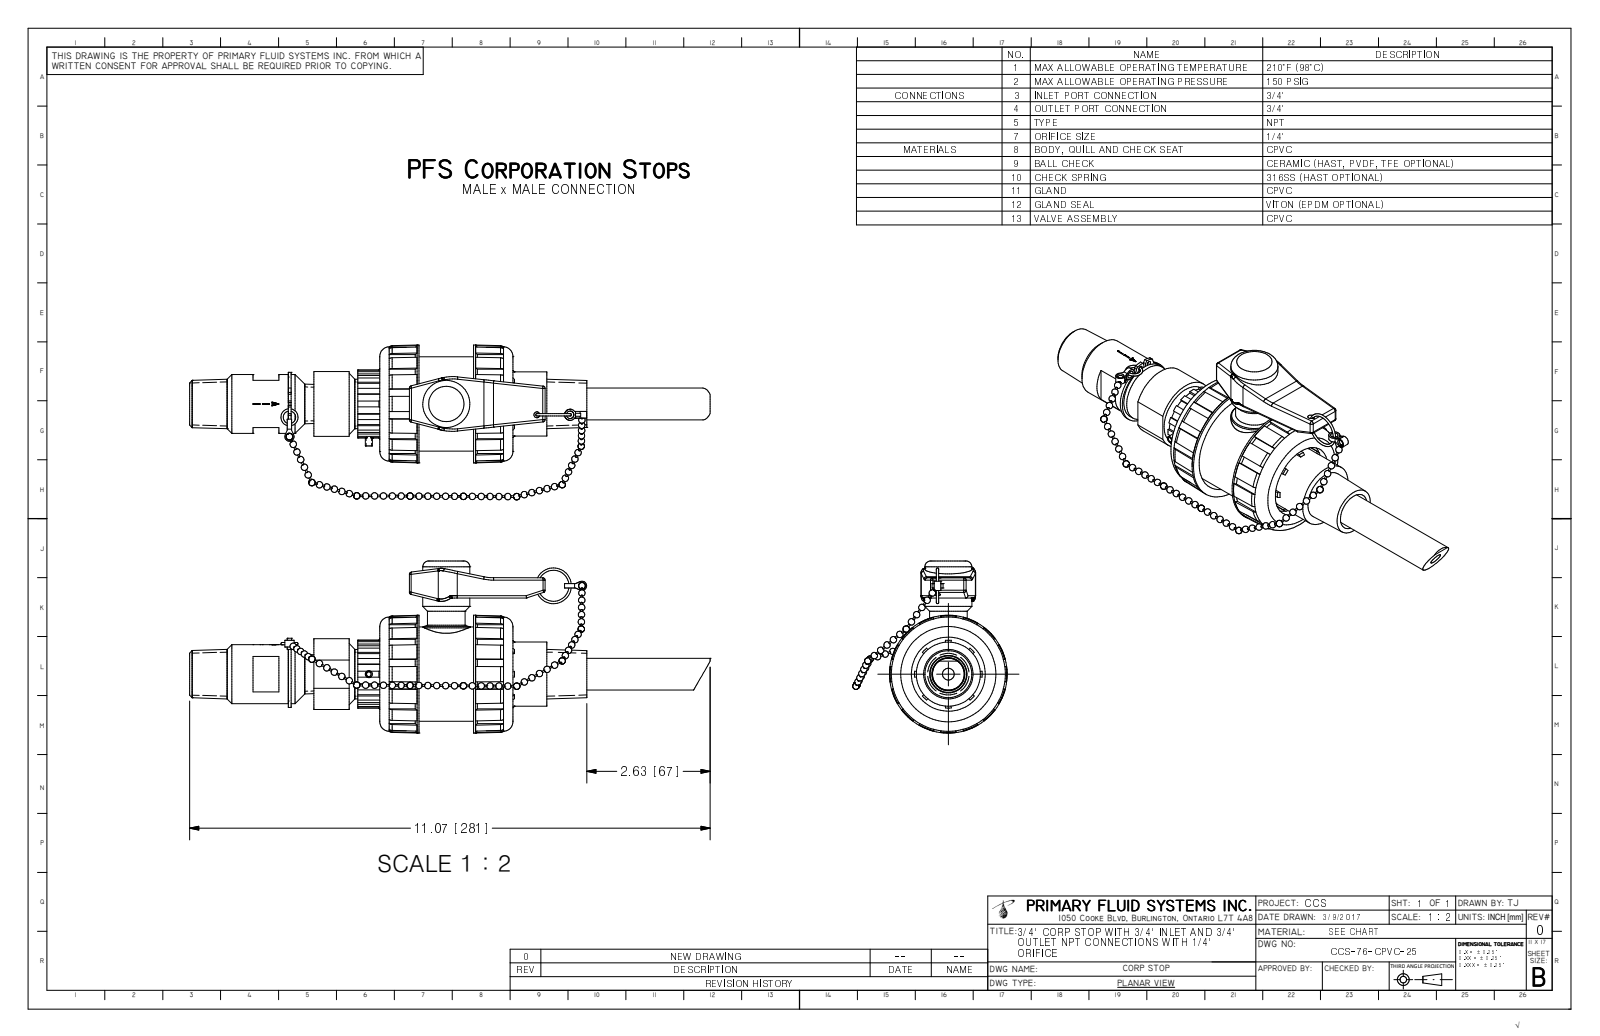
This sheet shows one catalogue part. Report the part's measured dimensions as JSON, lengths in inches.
{"part_name": "CCS-76-CPVC-25_R0", "step_written_by": "Autodesk Inventor 2009 (AUTOMOTIVE_DESIGN)", "units": "inches", "bodies": {"solids": 1, "faces": 603, "planar": 225, "cylindrical": 144, "other": 234}, "overall_size": [11.069, 3.65, 3.283], "volume_in3": 19.27, "surface_area_in2": 107.6, "round_holes": [[0.098, 1], [0.25, 1], [0.469, 1], [0.56, 1], [1.57, 1], [2.16, 1]], "round_bosses_or_shafts": [[2.5, 1], [2, 1], [1.801, 1], [1.36, 1], [1.343, 1], [1.25, 1], [1.14, 1], [1, 1]], "partial_cylinders_radius": [[0.05, 21], [1, 3], [0.054, 2], [0.197, 2], [0.351, 1], [0.624, 1], [0.72, 1], [0.75, 1]], "face_to_face_distances": [0.205, 2.625, 0.835, 1.995, 0.63, 1.79, 0.465, 2.83, 2.42, 1.16], "hole_center_spacings": [0.657]}
